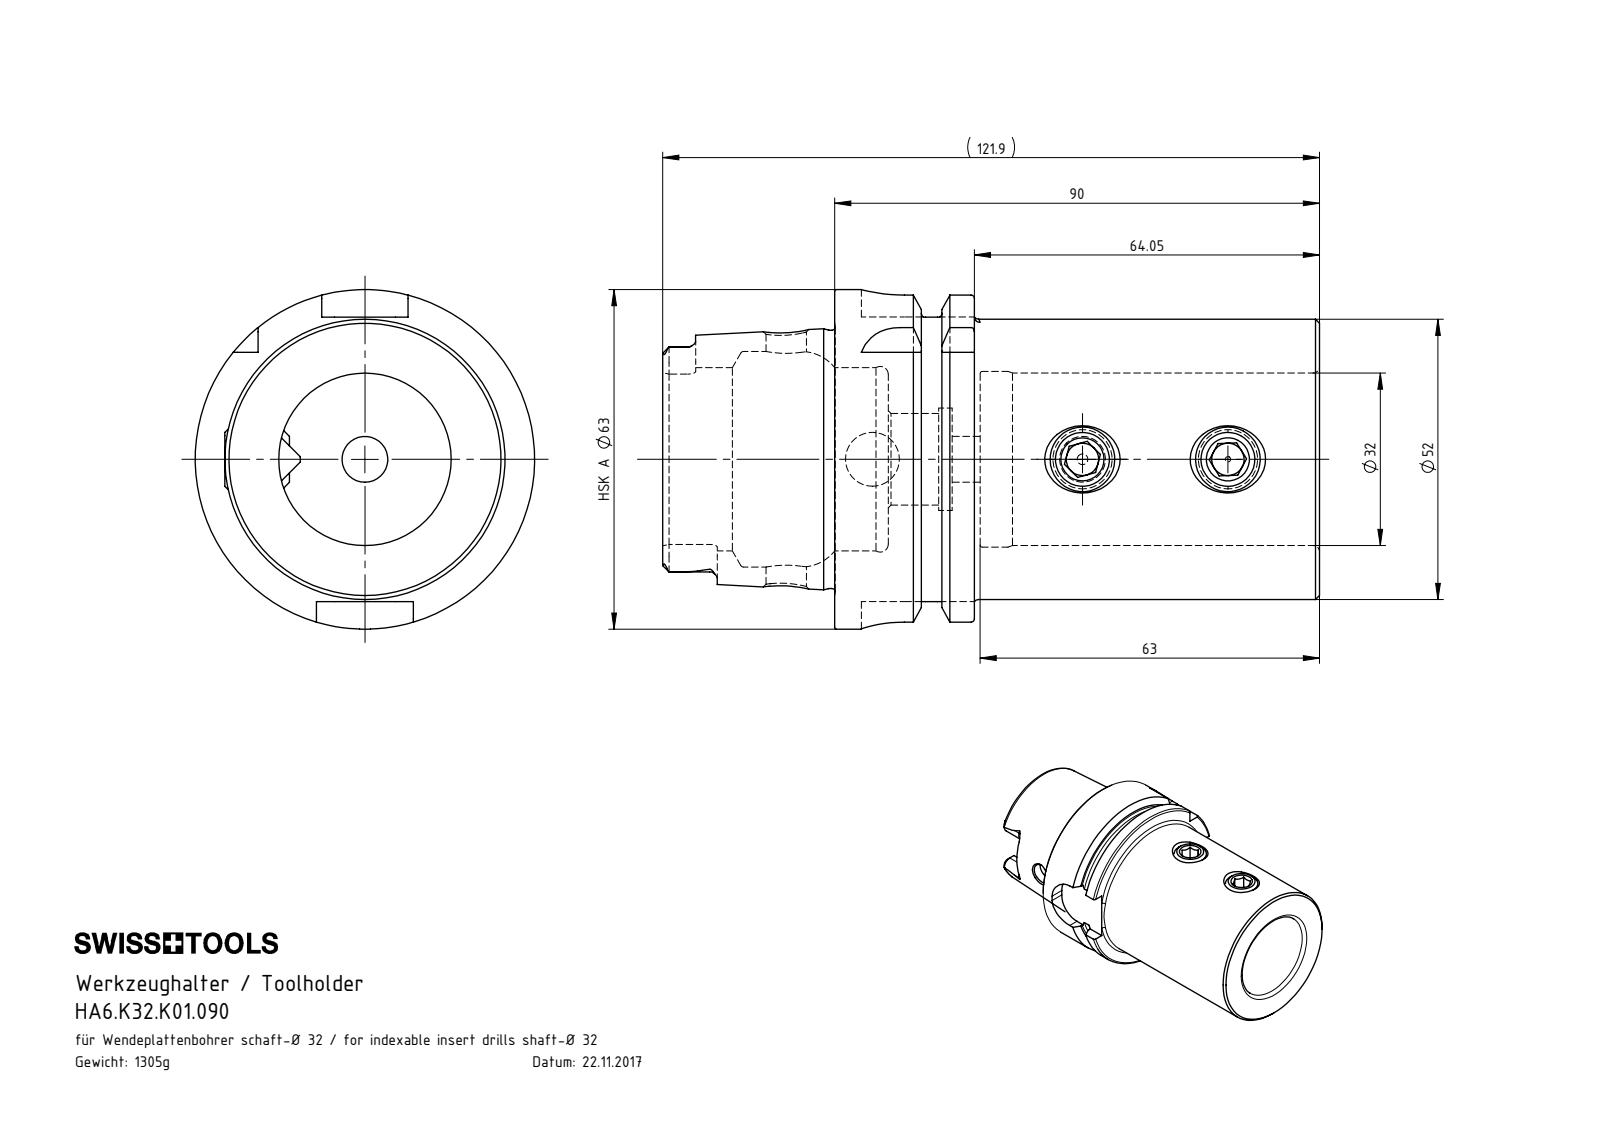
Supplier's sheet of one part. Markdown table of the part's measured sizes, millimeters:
| quantity | value |
| --- | --- |
| part name | HA6.K32.K01.090; K32-ER2.012.014_PreviewCfg; K32-ER1.012.012; HA6-K32.K01.090_B_Fertigbearbeitung |
| STEP written by | SolidWorks 2017 (AUTOMOTIVE_DESIGN) |
| units | millimeters |
| bodies | 3 solids, 231 faces (77 planar, 63 cylindrical, 91 other) |
| overall size | 121.9 × 63 × 63 |
| volume | 165 735 mm³ |
| surface area | 40 879 mm² |
| round holes (diameter × count) | 6 × 2, 10 × 2, 11 × 2, 7.5 × 1, 8.5 × 1, 17 × 1, 19 × 1, 32 × 1, 32.6 × 1, 34 × 1, 40 × 1 |
| round bosses / shafts (diameter × count) | 12 × 2, 63 × 1, 54.95 × 1, 52 × 1, 47.93 × 1 |
| partial cylindrical surfaces (radius × count) | 1.4 × 6, 2.88 × 4, 8 × 4 |
| main face-to-face distances | 90, 27, 63, 25.95, 1.05, 64.05, 16, 9.95, 17.05, 80.05 |
| hole center spacings | 27, 39, 66 |
